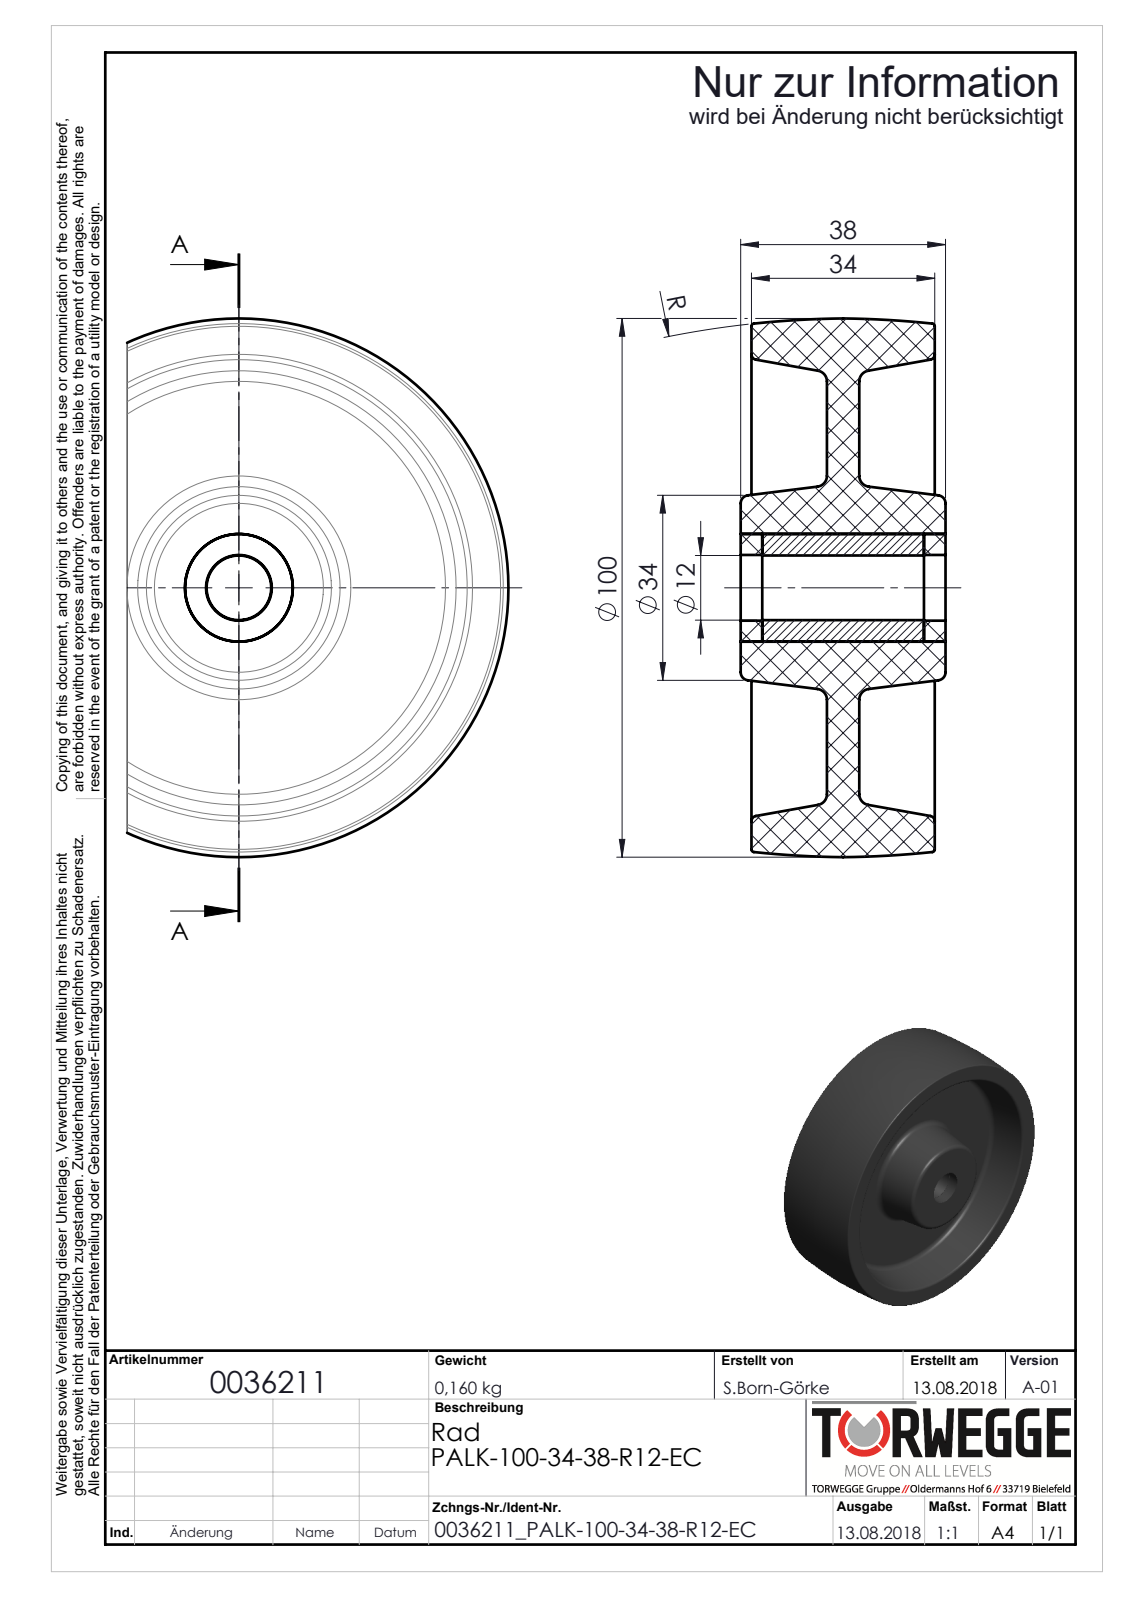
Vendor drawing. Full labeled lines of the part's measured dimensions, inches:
Part name (STEP PRODUCT): 0036211_PALK-100-34-38-R12-EC
STEP written by: SolidWorks 2018 (AUTOMOTIVE_DESIGN)
Units: inches
Bodies: 4 solids, 58 faces (12 planar, 14 cylindrical, 32 other)
Overall size (bounding box): 3.937 × 3.937 × 1.496
Volume: 8.666 in³ · Surface area: 63.5 in²
Round holes (diameter × count): ⌀0.472 ×1, ⌀0.48 ×1
Round bosses / shafts (diameter × count): ⌀0.787 ×1
Main face-to-face distances: 0.236, 0.551, 0.787, 1.339, 0.079, 0.63, 0.866, 1.417, 0.157, 1.26
